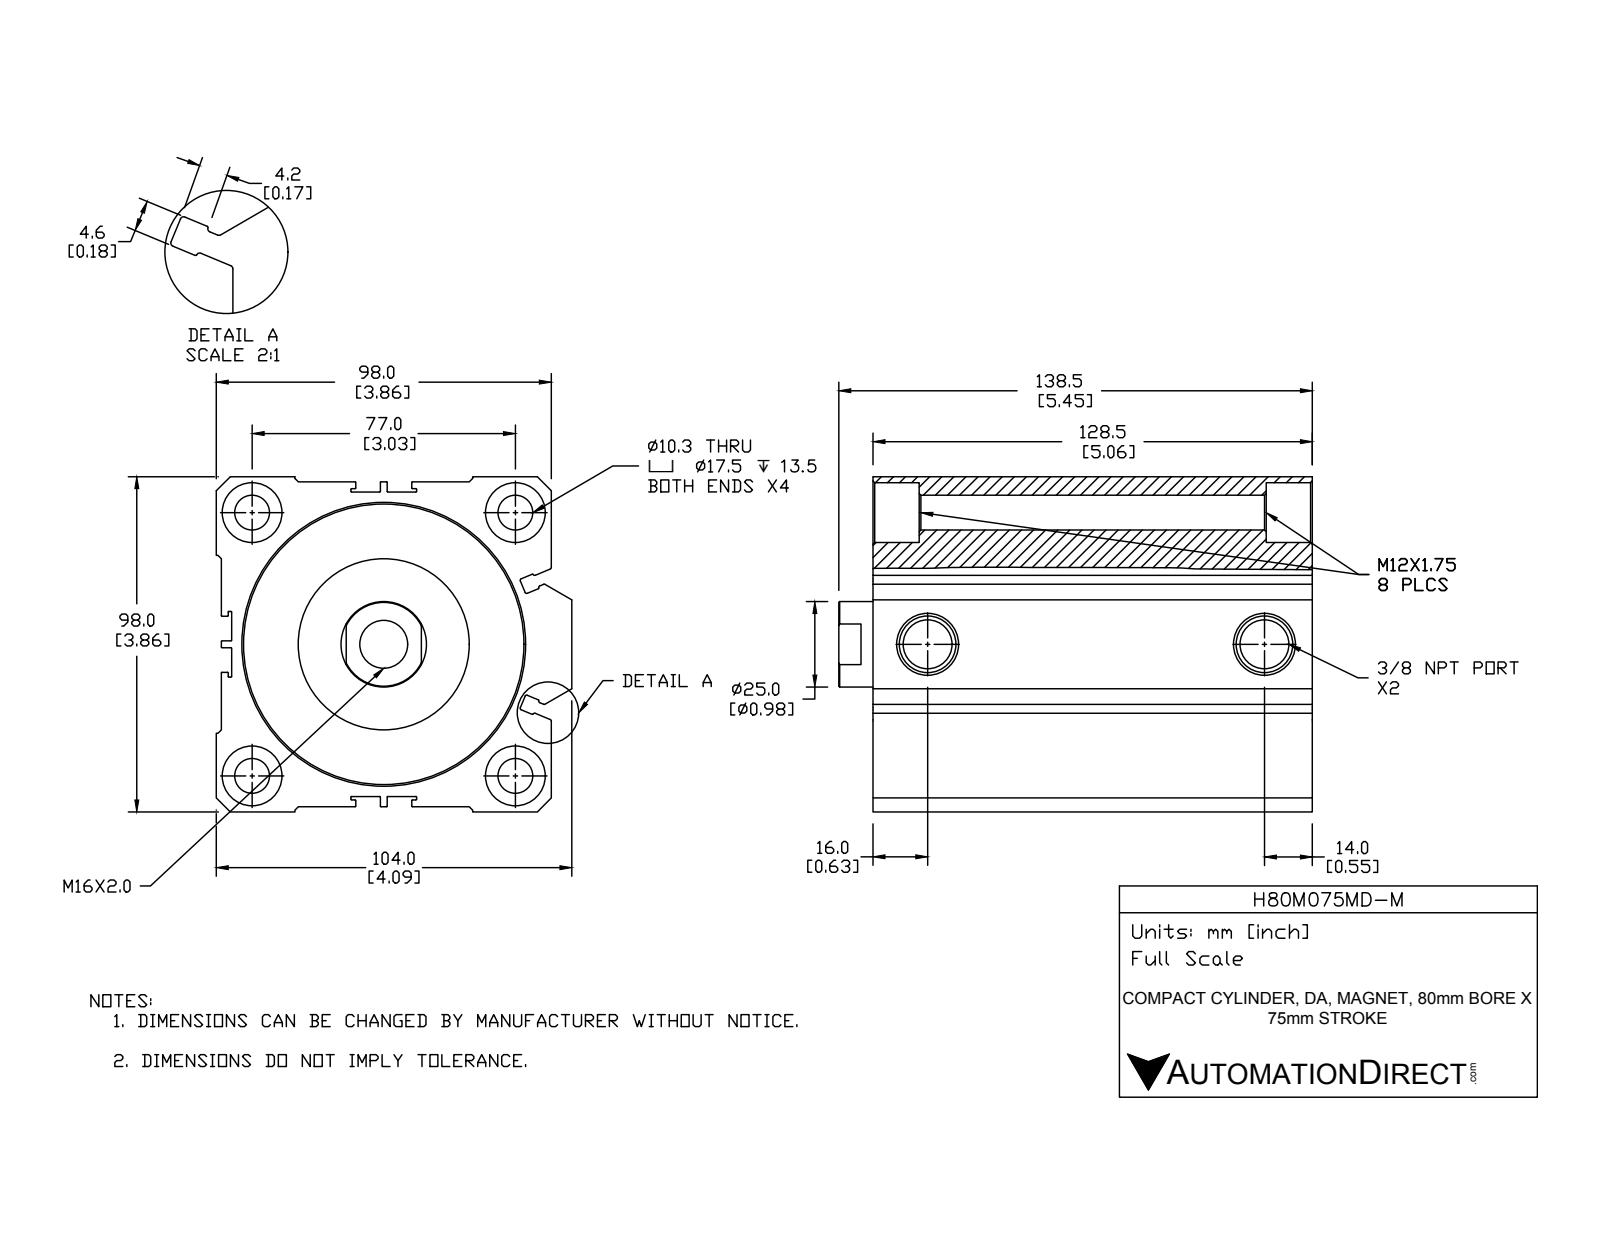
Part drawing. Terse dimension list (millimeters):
name: H80M075MD-M-PISTON; H80M075MD-M; H80M075MD-M-BODY
written by: SolidWorks 2015 (CONFIG_CONTROL_DESIGN)
unit: mm
bodies: 2 solids, 261 faces (105 planar, 103 cylindrical, 53 other)
size: 138.5 × 104 × 98
volume: 759 699 mm³; area: 164 371 mm²
holes: 4× ⌀10.2, 4× ⌀17.5, 2× ⌀14.27, 1× ⌀14, 1× ⌀25, 1× ⌀45.51, 1× ⌀80, 1× ⌀82
bosses: 1× ⌀50, 1× ⌀39
rounds: 40× R0.2, 12× R0.5
face distances: 96.5, 1.5, 98, 4.5, 3, 93.5, 75, 9, 2, 36.1
hole spacings: 54.45, 77, 108.89, 98.5
